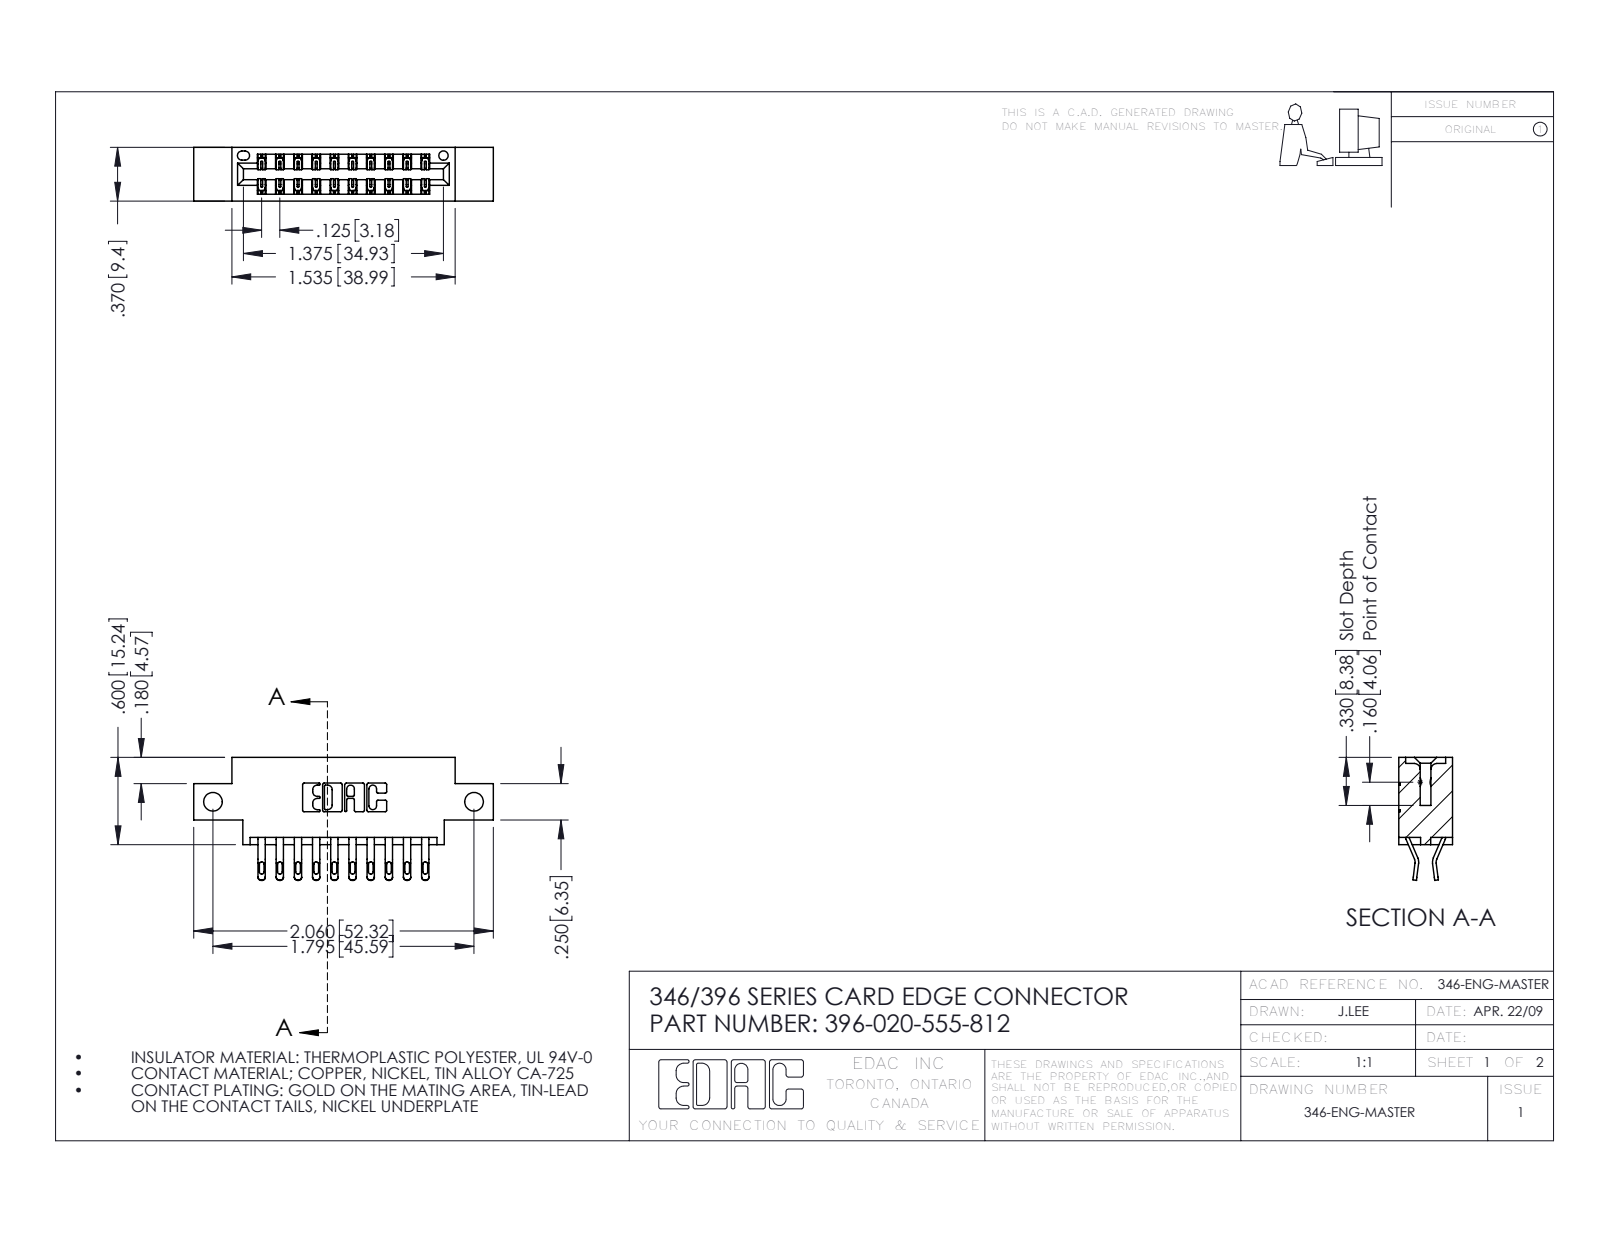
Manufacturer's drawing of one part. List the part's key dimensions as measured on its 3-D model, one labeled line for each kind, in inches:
Part name (STEP PRODUCT): 346 Part_0.170 Offset - Side Mount; 345-292-001_555 Tail; 396-020-555-812
STEP written by: SolidWorks 2016 (CONFIG_CONTROL_DESIGN)
Units: inches
Bodies: 21 solids, 1286 faces (740 planar, 546 cylindrical, 0 other)
Overall size (bounding box): 2.06 × 0.845 × 0.37
Volume: 0.285 in³ · Surface area: 9.556 in²
Round holes (diameter × count): ⌀0.128 ×2, ⌀0.064 ×1
Partial cylindrical surfaces — rounded edges, fillets, slot ends (radius × count): R0.016 ×40, R0.02 ×40, R0.006 ×30, R0.01 ×22, R0.007 ×6, R0.031 ×6, R0.026 ×3, R0.01 ×2
Main face-to-face distances: 0.25, 0.37, 0.048, 0.322, 0.025, 0.072, 0.298, 0.275, 0.148, 0.222
Hole centre spacings: 1.795
